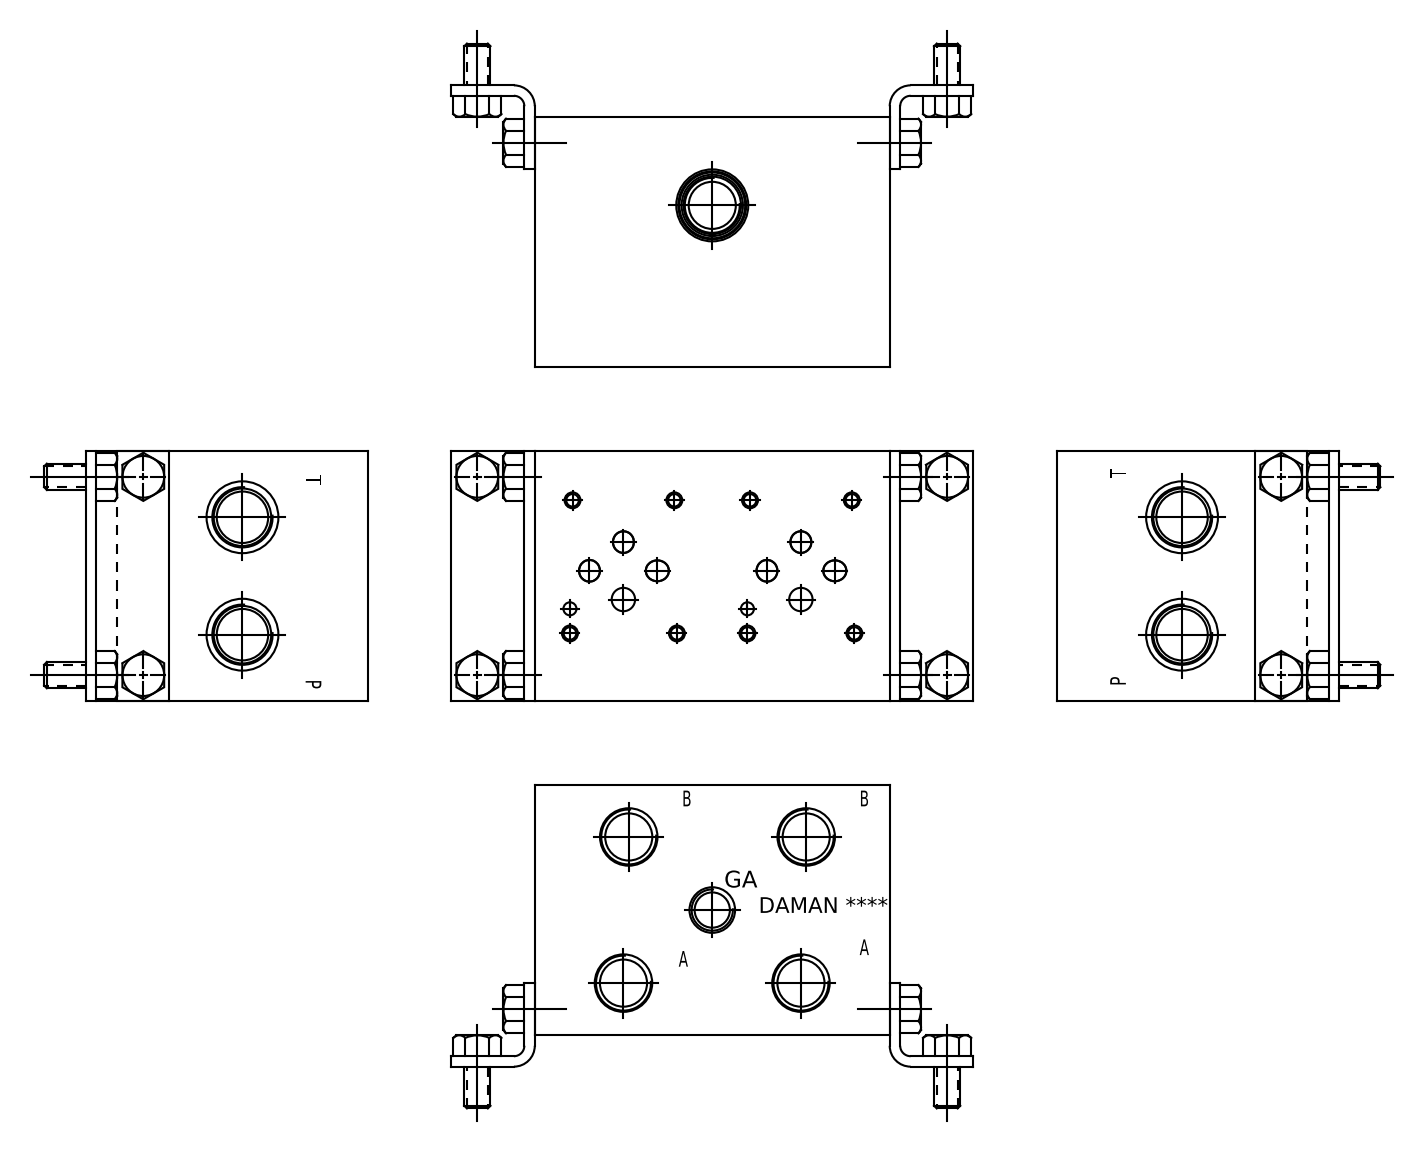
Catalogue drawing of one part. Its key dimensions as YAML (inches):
part_name: "Part_AD03S022P~S_3D"
step_written_by: "Autodesk Inventor 2019 (AUTOMOTIVE_DESIGN)"
units: inches
bodies: {solids: 1, faces: 634, planar: 355, cylindrical: 62, other: 217}
overall_size: [4.25, 3, 3]
volume: 33.88
surface_area: 97.88
round_holes:
  - {diameter: 0.149, count: 8}
  - {diameter: 0.19, count: 8}
  - {diameter: 0.25, count: 6}
  - {diameter: 0.563, count: 4}
  - {diameter: 0.681, count: 4}
  - {diameter: 0.156, count: 2}
  - {diameter: 0.257, count: 2}
  - {diameter: 0.281, count: 2}
  - {diameter: 0.312, count: 2}
  - {diameter: 0.625, count: 2}
  - {diameter: 0.688, count: 2}
  - {diameter: 0.85, count: 2}
face_to_face_distances: [3, 4.25, 0.605, 3.645, 0.462, 2.538, 3.04, 0.039, 2.961, 2.499]
hole_center_spacings: [2.125, 0.868, 1.321, 1.594, 2.026, 2.125, 2.233, 0.295]
